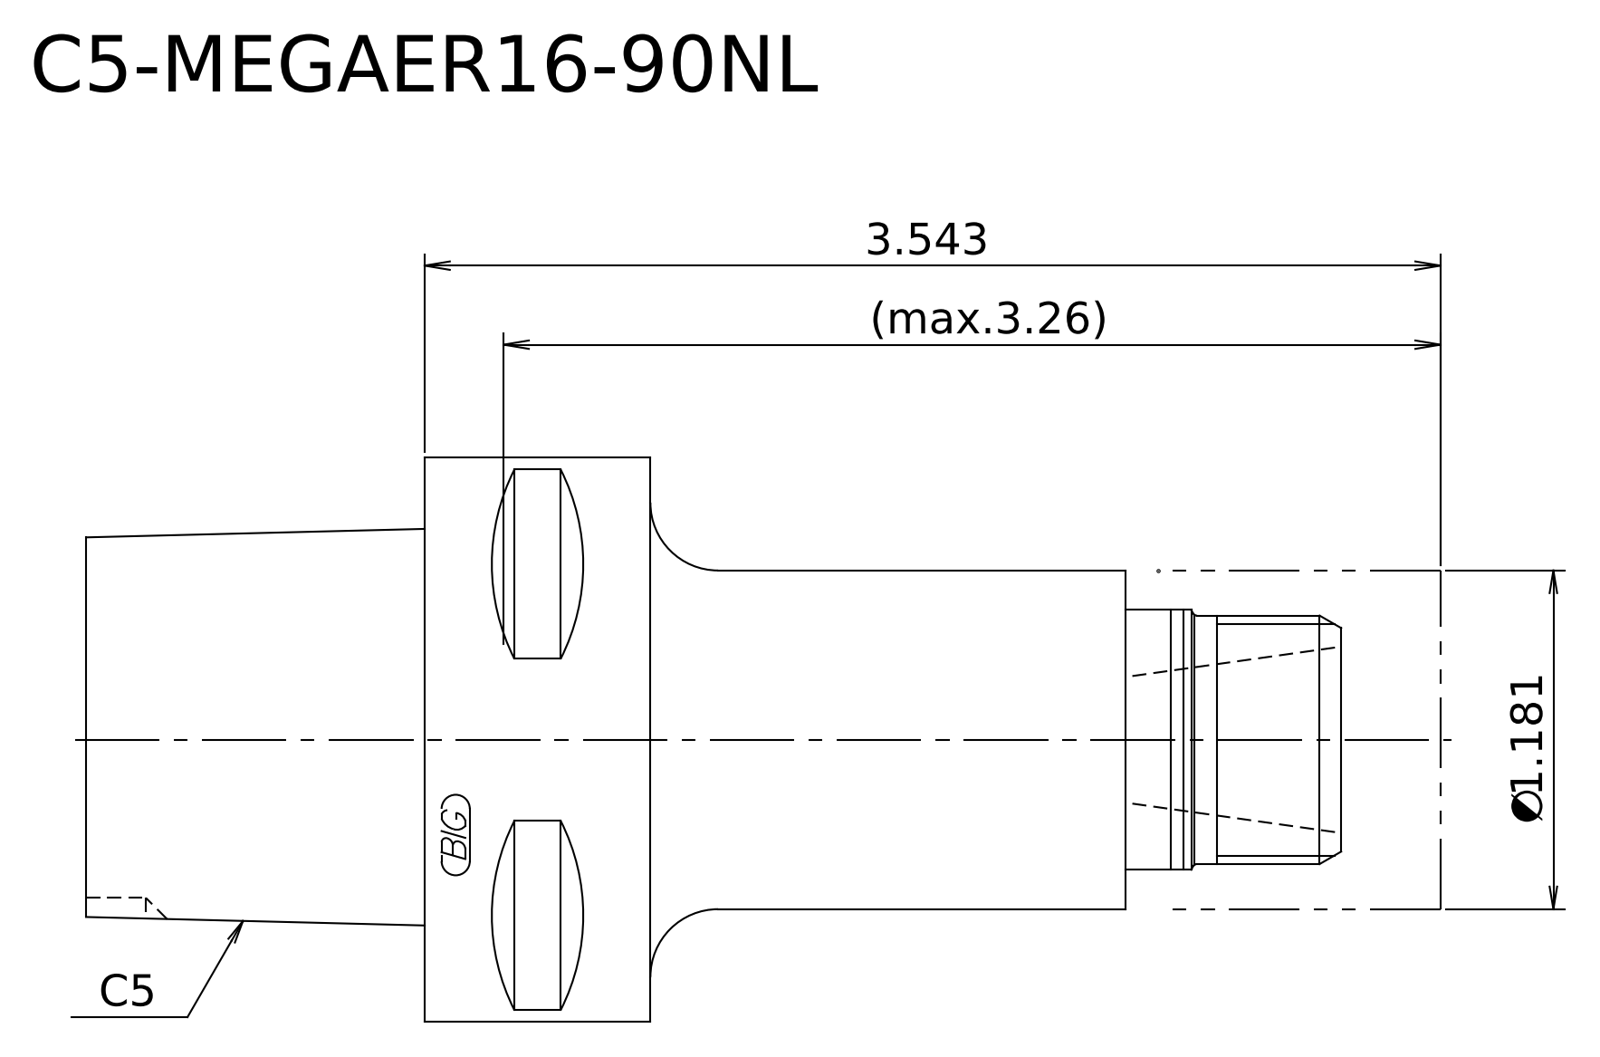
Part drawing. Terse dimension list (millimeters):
written by: Kubotek KeyCreator 2011 V10.0.2 (22737) (automotive_design)
unit: mm
bodies: 2 solids, 16 faces (7 planar, 5 cylindrical, 4 other)
size: 120 × 50 × 50
volume: 123 232 mm³; area: 18 948 mm²
bosses: 1× ⌀50, 1× ⌀30, 1× ⌀23, 1× ⌀22
face distances: 30, 65, 95, 25, 90, 120, 70, 45, 20, 50
